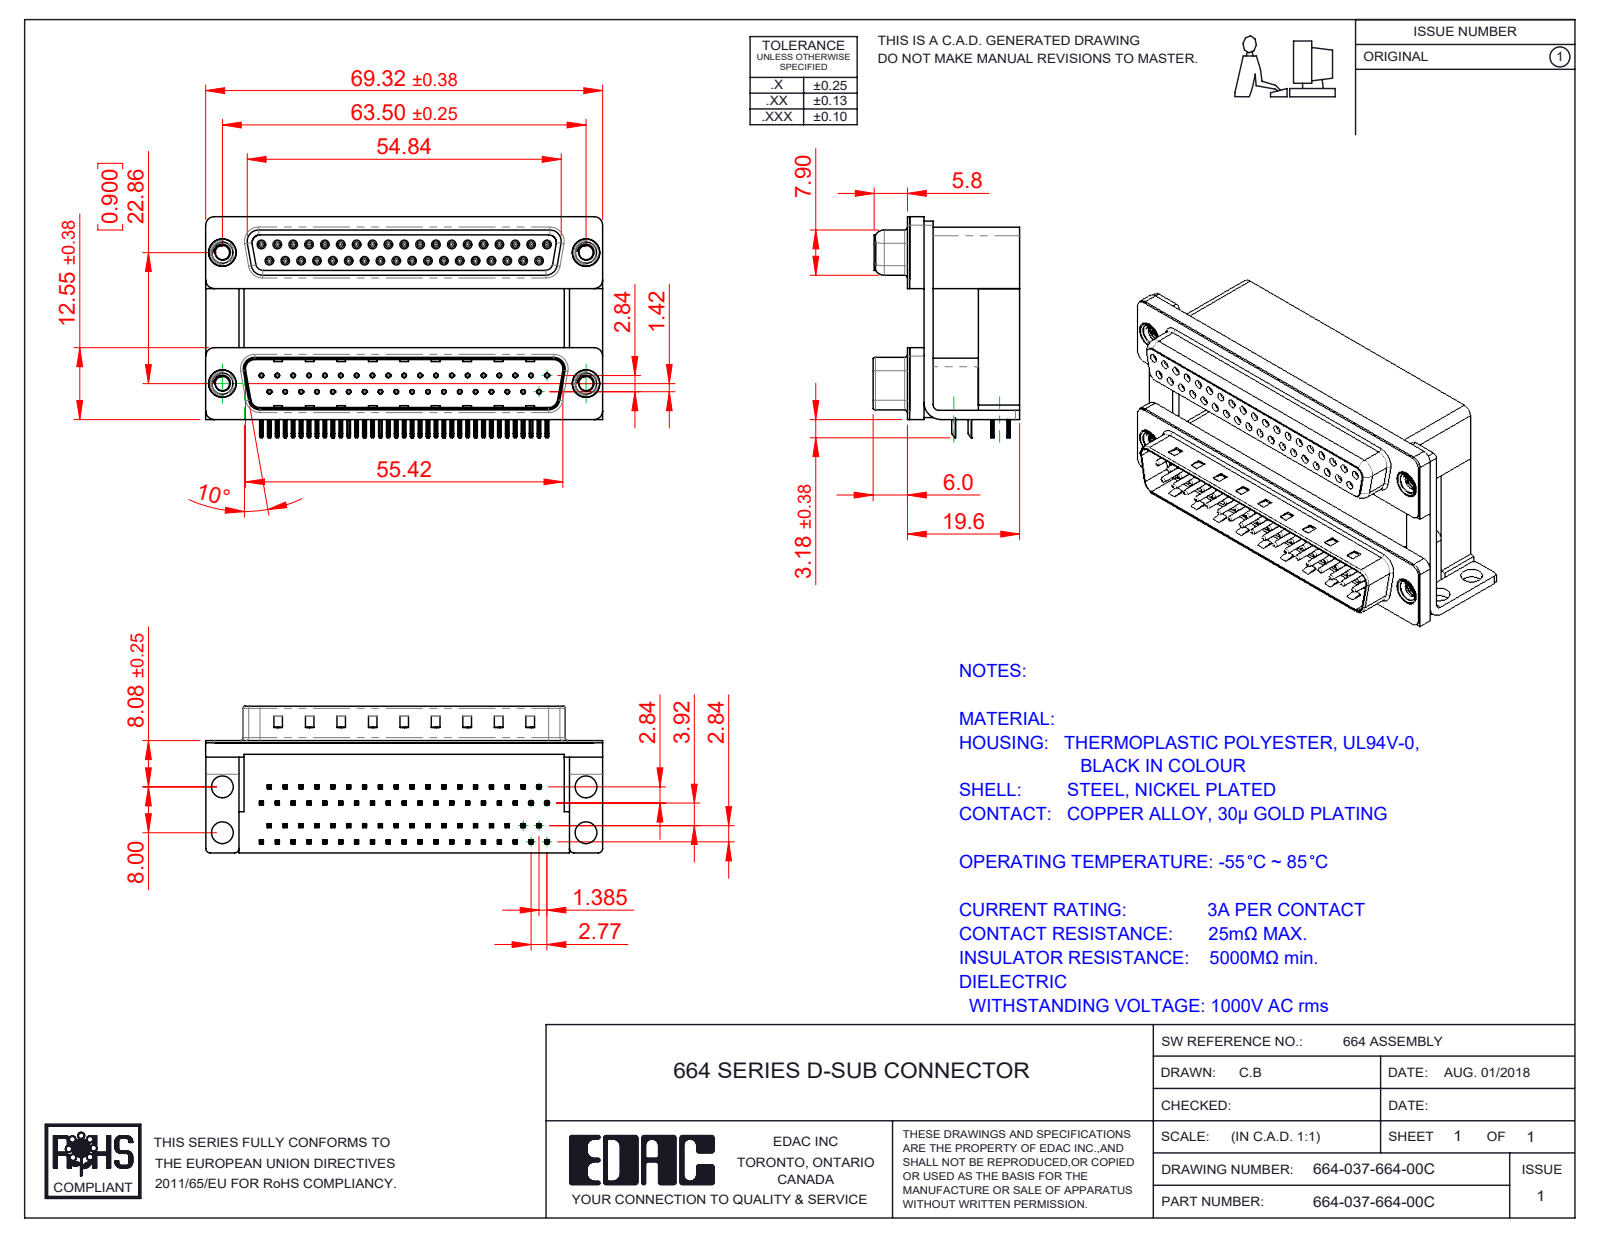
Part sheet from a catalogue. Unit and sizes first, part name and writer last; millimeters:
Units: millimetres
Overall size (bounding box): 69.32 × 38.59 × 25.6
Round holes (diameter × count): ⌀0.8 ×74, ⌀0.35 ×37, ⌀0.9 ×37, ⌀2.5 ×4, ⌀3.5 ×4, ⌀3.8 ×4, ⌀4 ×4, ⌀4.8 ×4, ⌀5 ×4
Round bosses / shafts (diameter × count): ⌀1.2 ×37, ⌀0.75 ×37, ⌀4.9 ×4, ⌀4.75 ×4, ⌀3.9 ×4
Partial cylindrical surfaces — rounded edges, fillets, slot ends (radius × count): R0.1 ×296, R0.15 ×148, R0.25 ×148, R0.12 ×74, R0.35 ×74, R0.34 ×37, R0.28 ×18, R1.5 ×13
Main face-to-face distances: 19.2, 0.4, 12, 7.2, 2.19, 2.84, 0.65, 22.5, 10.69, 0.45
Hole centre spacings: 2.77, 5.54, 3.16, 8.31, 11.08, 13.85, 16.62, 19.39
Volume: 32 651 mm³ · Surface area: 34 047 mm²
Bodies: 85 solids, 8949 faces (4741 planar, 2185 cylindrical, 2023 other)
Part name (STEP PRODUCT): 664 Contact Bottom Lower; 664 Housing Upper_37 Contacts H; 664 Mounting Bracket_NoneH; 664 Contact Top Lower (+8 more)
STEP written by: SolidWorks 2020 (CONFIG_CONTROL_DESIGN)
